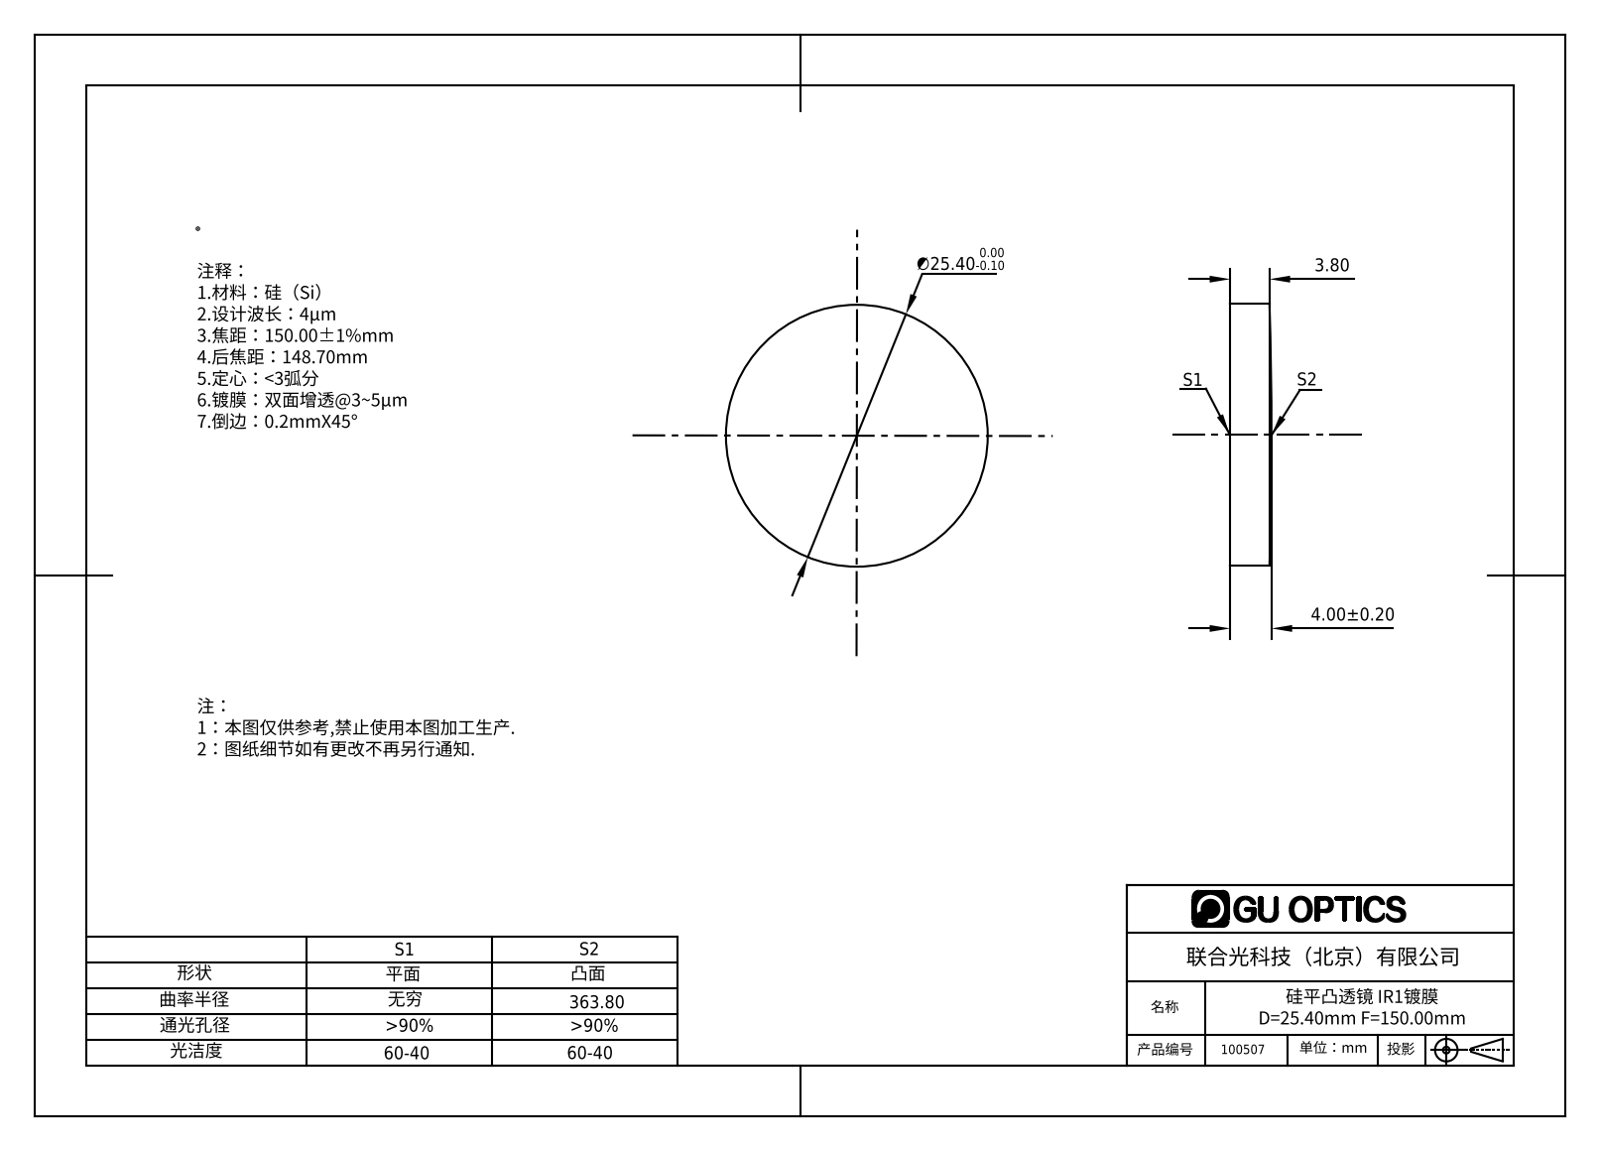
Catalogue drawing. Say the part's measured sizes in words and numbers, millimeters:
The part is named "100495". Its 3-D file was written by "SolidWorks 2016 (AUTOMOTIVE_DESIGN)". It is 1 solid with 5 faces: 1 planar, 2 cylindrical and 2 other. Overall it measures 25.4 by 25.4 by 4 millimeters. Its volume is 1 976 cubic millimeters and its surface area 1 317 square millimeters. Round bosses or shafts: 1 of diameter 25.4.
